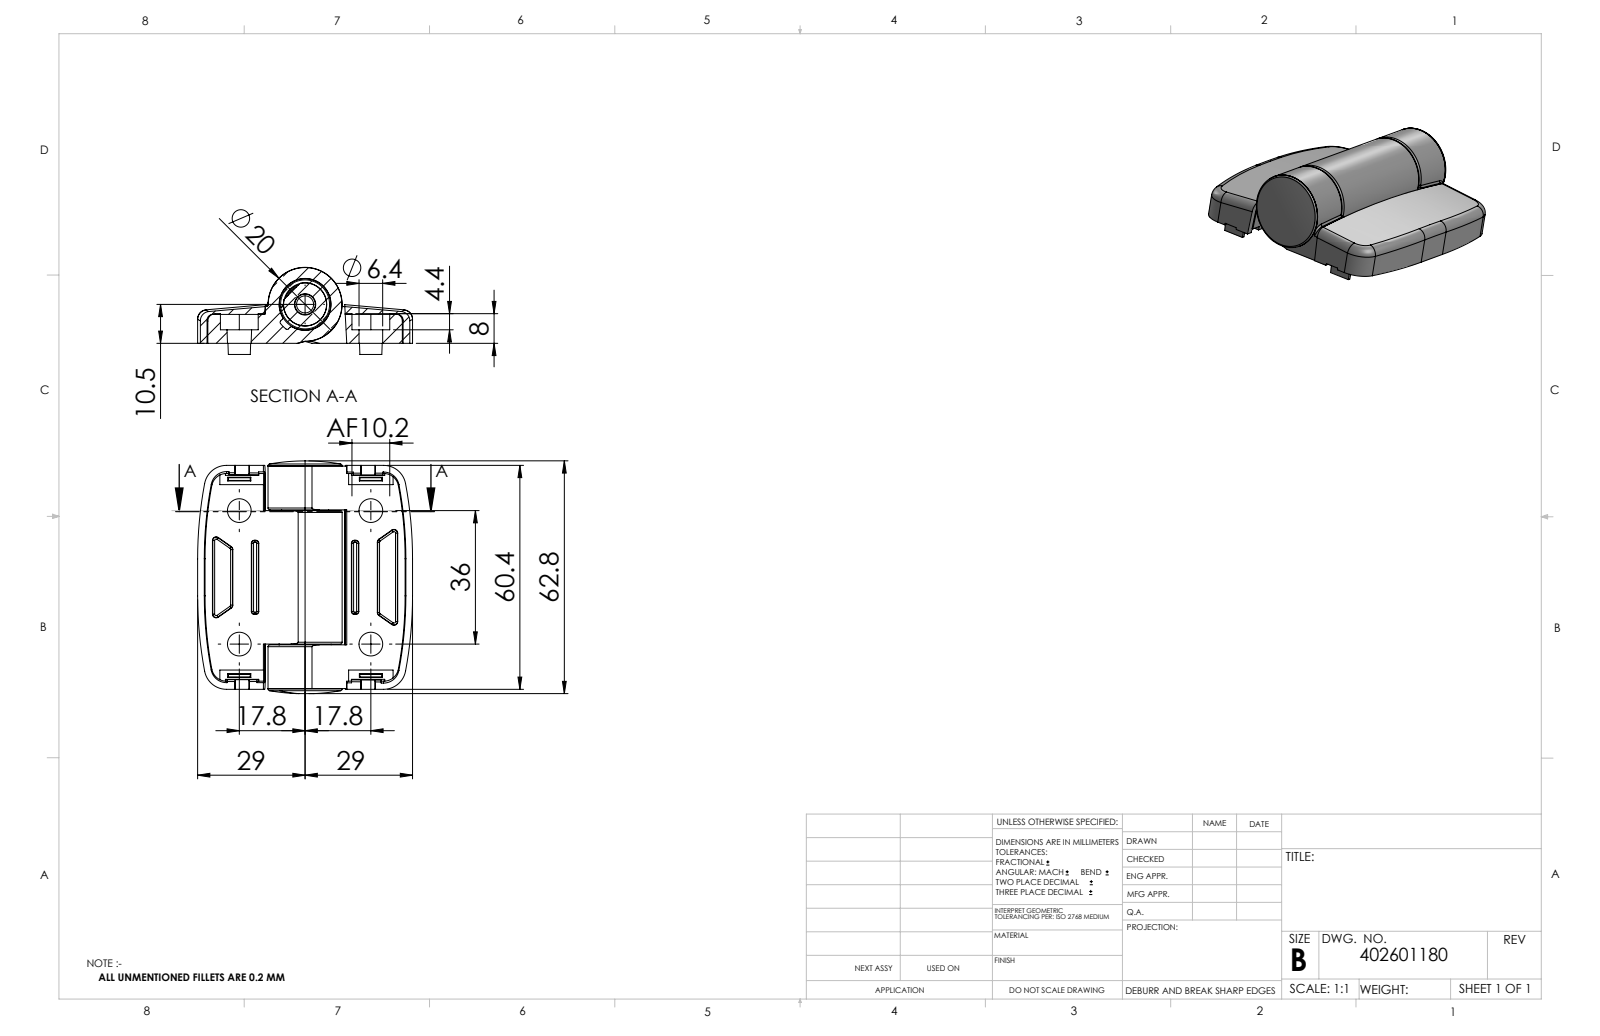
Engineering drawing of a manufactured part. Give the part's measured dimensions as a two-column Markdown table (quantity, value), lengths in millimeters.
| quantity | value |
| --- | --- |
| part name | 402601180_c_1 |
| STEP written by | SolidWorks 2014 (CONFIG_CONTROL_DESIGN) |
| units | millimeters |
| bodies | 9 solids, 693 faces (254 planar, 183 cylindrical, 256 other) |
| overall size | 62.76 × 58 × 23.5 |
| volume | 33 738 mm³ |
| surface area | 30 714 mm² |
| round holes (diameter × count) | 6.4 × 2, 4.6 × 1, 5.5 × 1, 8 × 1, 11.89 × 1, 14 × 1 |
| round bosses / shafts (diameter × count) | 20 × 1 |
| partial cylindrical surfaces (radius × count) | 0.5 × 48, 0.3 × 8, 0.2 × 6, 1.5 × 6, 2.5 × 6, 2 × 4, 4 × 4, 4.2 × 4 |
| main face-to-face distances | 7.8, 8, 12, 48.2, 2, 1.8, 10.2, 1, 48, 11.8 |
| hole center spacings | 36 |
